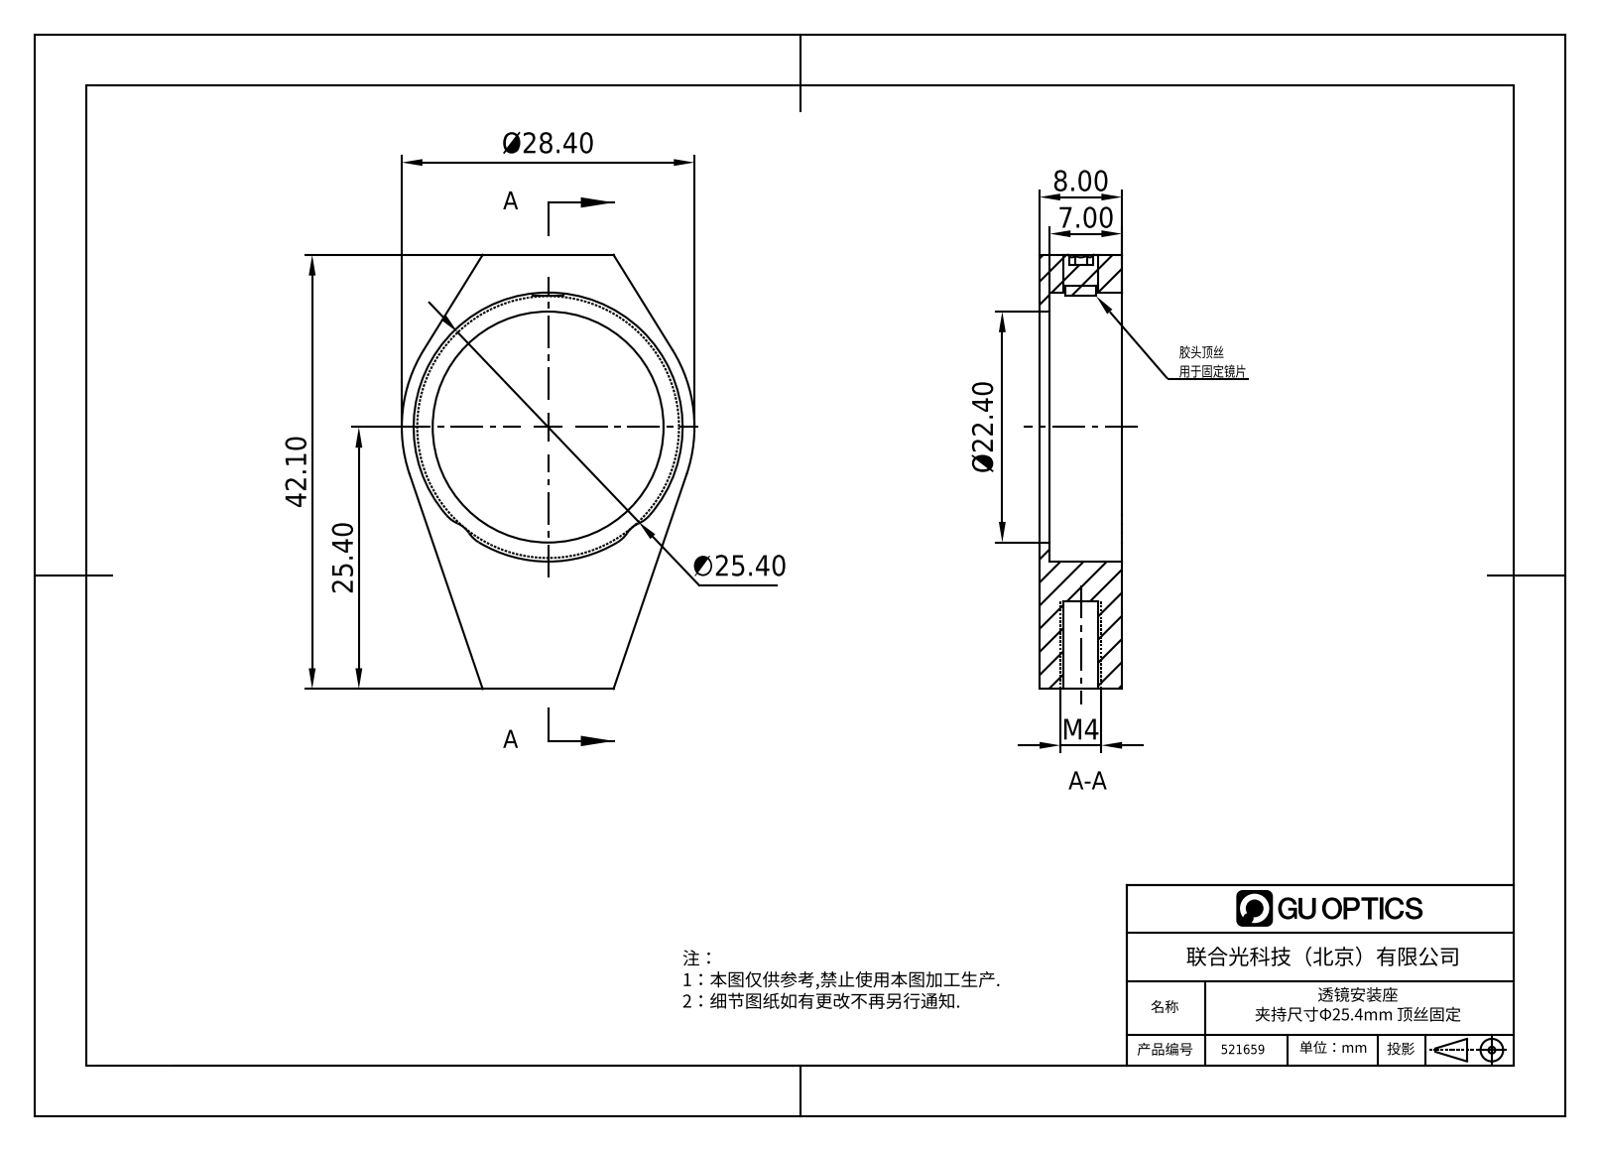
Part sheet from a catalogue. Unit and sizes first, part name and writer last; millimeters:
Units: millimetres
Overall size (bounding box): 42.1 × 28.4 × 8
Round holes (diameter × count): ⌀3.3 ×1, ⌀22.4 ×1, ⌀26.1 ×1
Round bosses / shafts (diameter × count): ⌀3 ×1
Partial cylindrical surfaces — rounded edges, fillets, slot ends (radius × count): R3 ×4, R2.5 ×2, R14.2 ×1
Main face-to-face distances: 8, 1, 7, 42.1, 38.1, 4, 41.1, 3, 2
Bodies: 0 solids, 43 faces (18 planar, 21 cylindrical, 4 other)
Part name (STEP PRODUCT): 1.3.1.19_ZZT-1.0-D
STEP written by: SolidWorks 2021 (CONFIG_CONTROL_DESIGN)
